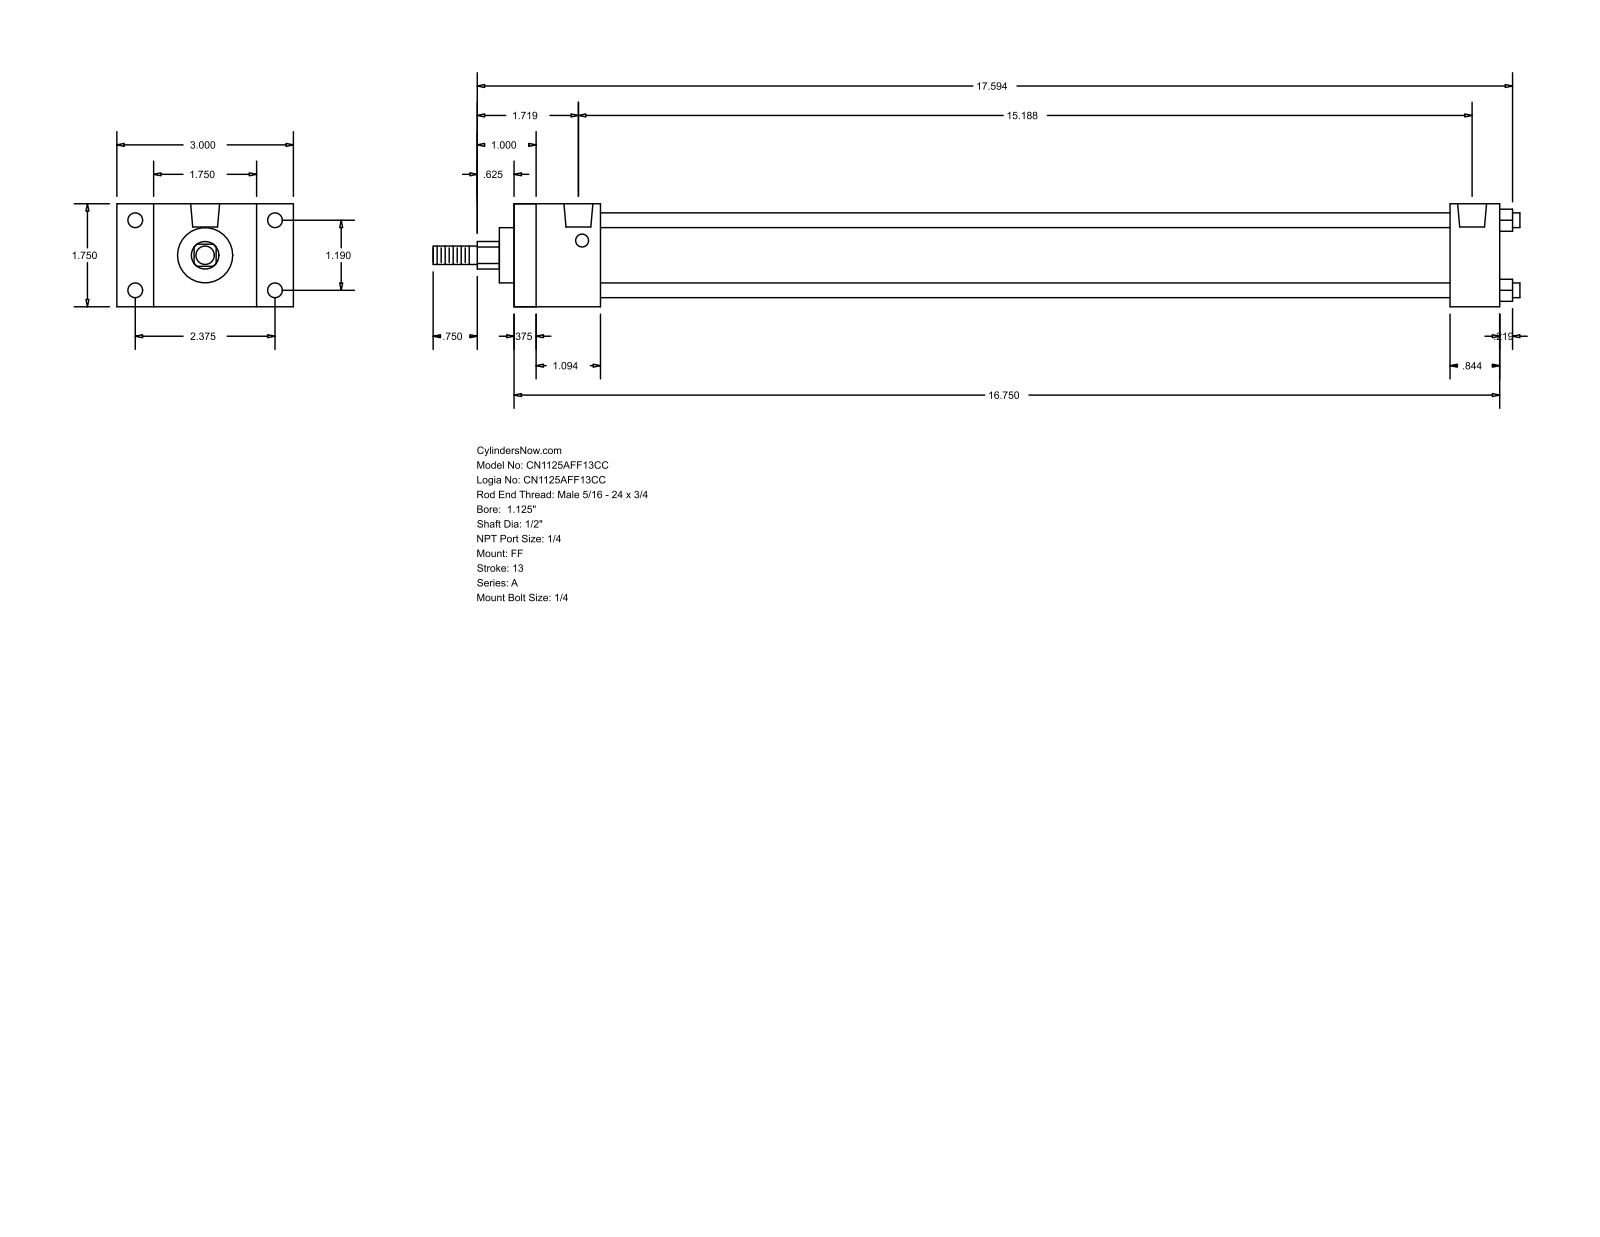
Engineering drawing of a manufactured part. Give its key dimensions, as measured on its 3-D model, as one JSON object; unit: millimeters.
{"part_name": "A_FF__0112_0.5", "step_written_by": "GSSL Pune (CONFIG_CONTROL_DESIGN)", "units": "millimeters", "bodies": {"solids": 0, "faces": 92, "planar": 64, "cylindrical": 28, "other": 0}, "overall_size": [469.11, 76.2, 44.45], "round_holes": [[5.56, 4], [6.35, 4], [12.49, 2]], "round_bosses_or_shafts": [[6.35, 4], [31.88, 1], [23.81, 1], [12.7, 1], [7.94, 1]], "partial_cylinders_radius": [[5.94, 1]], "face_to_face_distances": [44.46, 425.44, 9.52, 415.92, 15.87, 404.01, 394.49, 21.43, 37.3, 27.78], "hole_center_spacings": [30.22, 60.32, 67.47, 382.59, 1.58, 1.59, 384.17, 384.18]}
